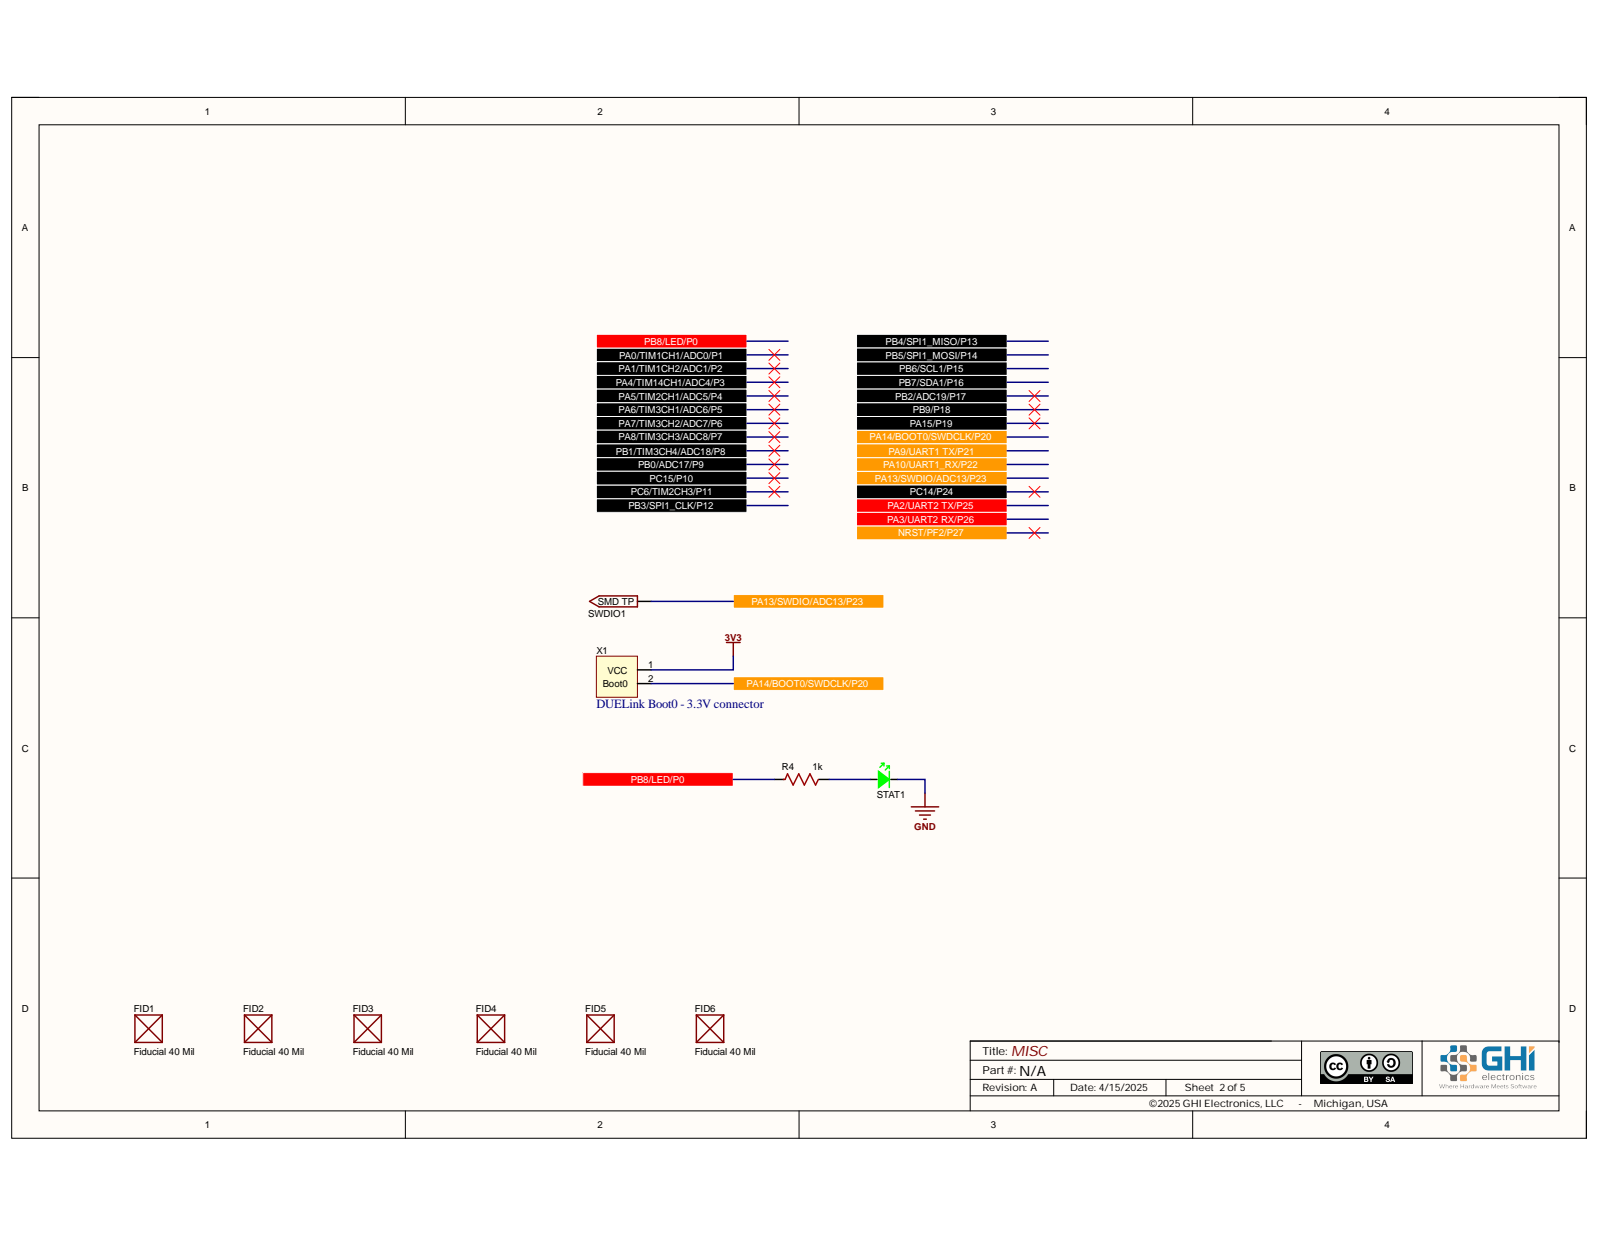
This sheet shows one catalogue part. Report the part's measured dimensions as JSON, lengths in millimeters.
{"part_name": "PCB; Board; STAT1; 0603 LED Green (+5 more)", "step_written_by": "Open CASCADE 7.5 (AUTOMOTIVE_DESIGN)", "units": "millimeters", "bodies": {"solids": 112, "faces": 2236, "planar": 1418, "cylindrical": 558, "other": 260}, "overall_size": [25, 22, 18.02], "volume_mm3": 1771, "surface_area_mm2": 3122, "round_holes": [[1.02, 8], [1.02, 2], [3, 2]], "partial_cylinders_radius": [[0.12, 35], [0.15, 14], [0.17, 2], [0.18, 2], [0.18, 2], [1, 2], [3.5, 2]], "face_to_face_distances": [1.6, 2, 12, 13.6, 10, 11.6, 2.54, 0.64, 0.68, 22], "hole_center_spacings": [2.54, 5.08, 7.62, 10.16, 12.7, 5.62, 5.67, 6.62]}
